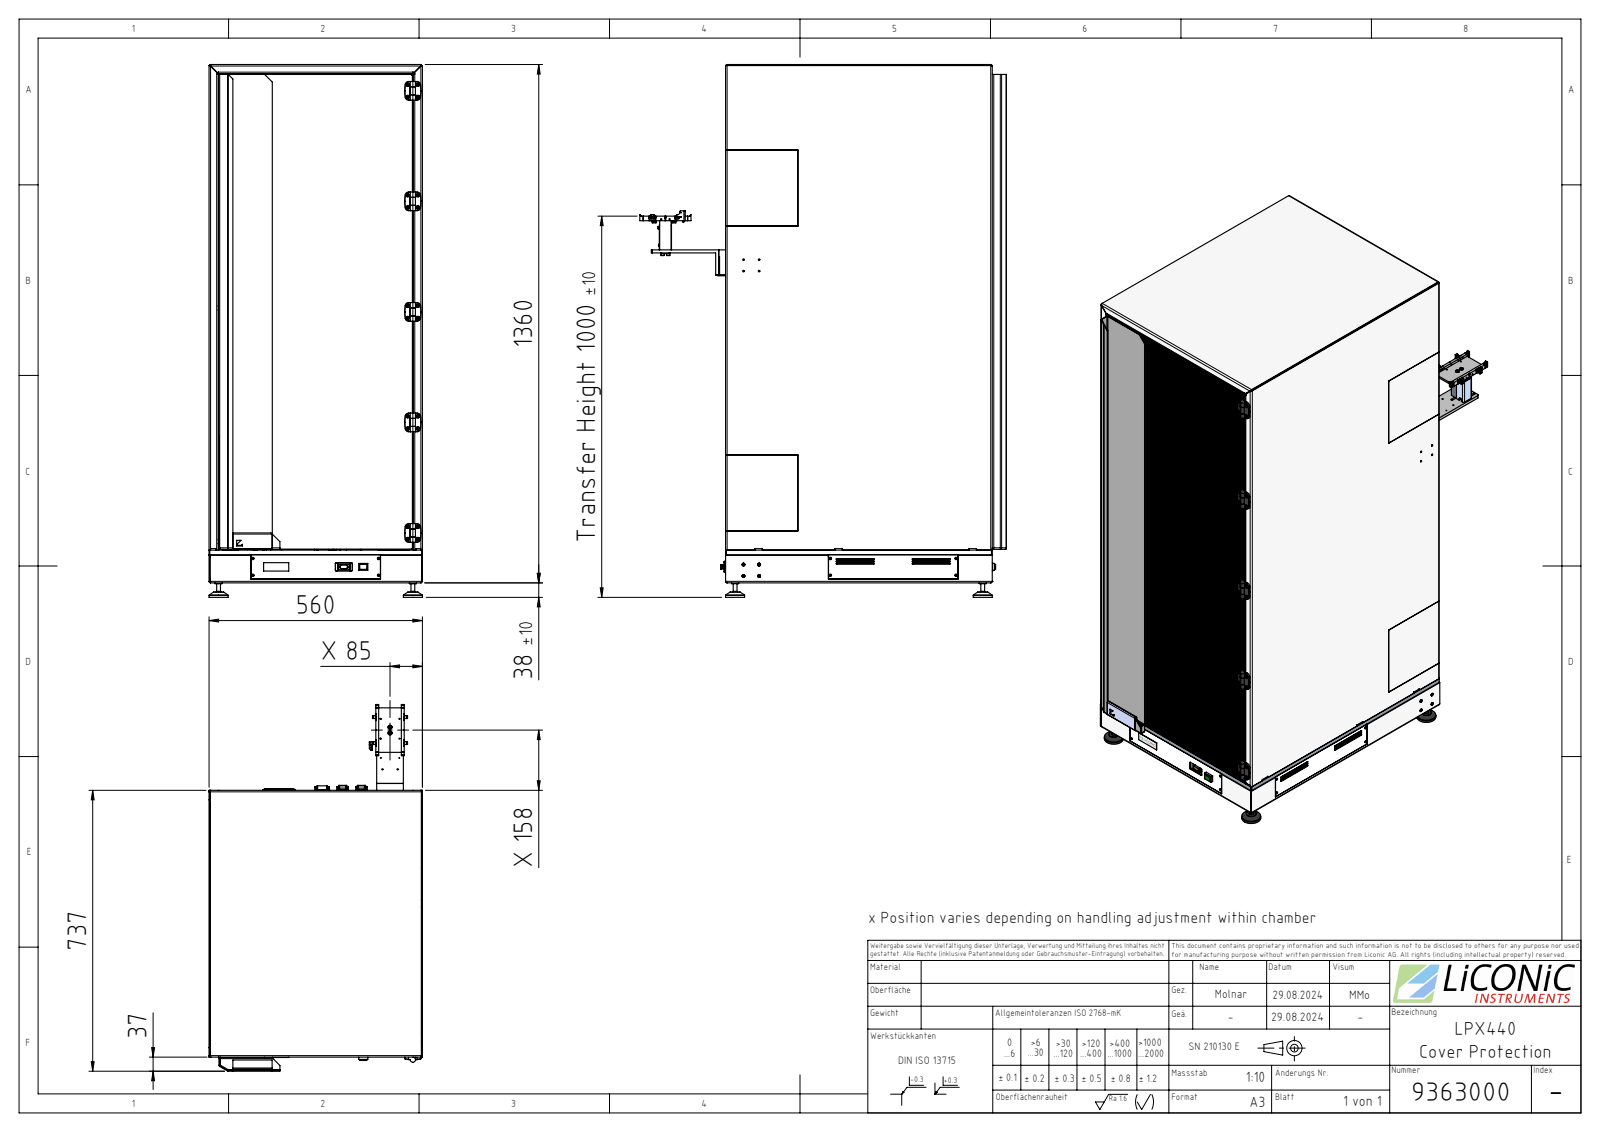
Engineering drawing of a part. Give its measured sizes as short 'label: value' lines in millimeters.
name: 9363000
written by: SolidWorks 2022 (AUTOMOTIVE_DESIGN)
unit: mm
bodies: 72 solids, 9071 faces (4870 planar, 3974 cylindrical, 227 other)
size: 1398 × 962.17 × 560.01
volume: 23 050 000 mm³; area: 12 570 000 mm²
holes: 88× ⌀4, 74× ⌀4.2, 62× ⌀2.5, 47× ⌀3.3, 32× ⌀6.5, 27× ⌀4.5, 20× ⌀9, 16× ⌀3.4, 16× ⌀7.1, 14× ⌀6, 11× ⌀5, 11× ⌀6.2
bosses: 8× ⌀22, 4× ⌀50.01, 4× ⌀10, 3× ⌀1.5, 1× ⌀540, 1× ⌀234, 1× ⌀15.5, 1× ⌀14.5
rounds: 832× R0.1, 832× R0.25, 487× R2, 127× R5, 114× R2.5, 84× R1, 38× R3, 36× R1.5
face distances: 2, 558, 560, 556, 700, 693, 698, 1358, 5, 695
hole spacings: 23, 46, 69, 92, 115, 138, 161, 184
